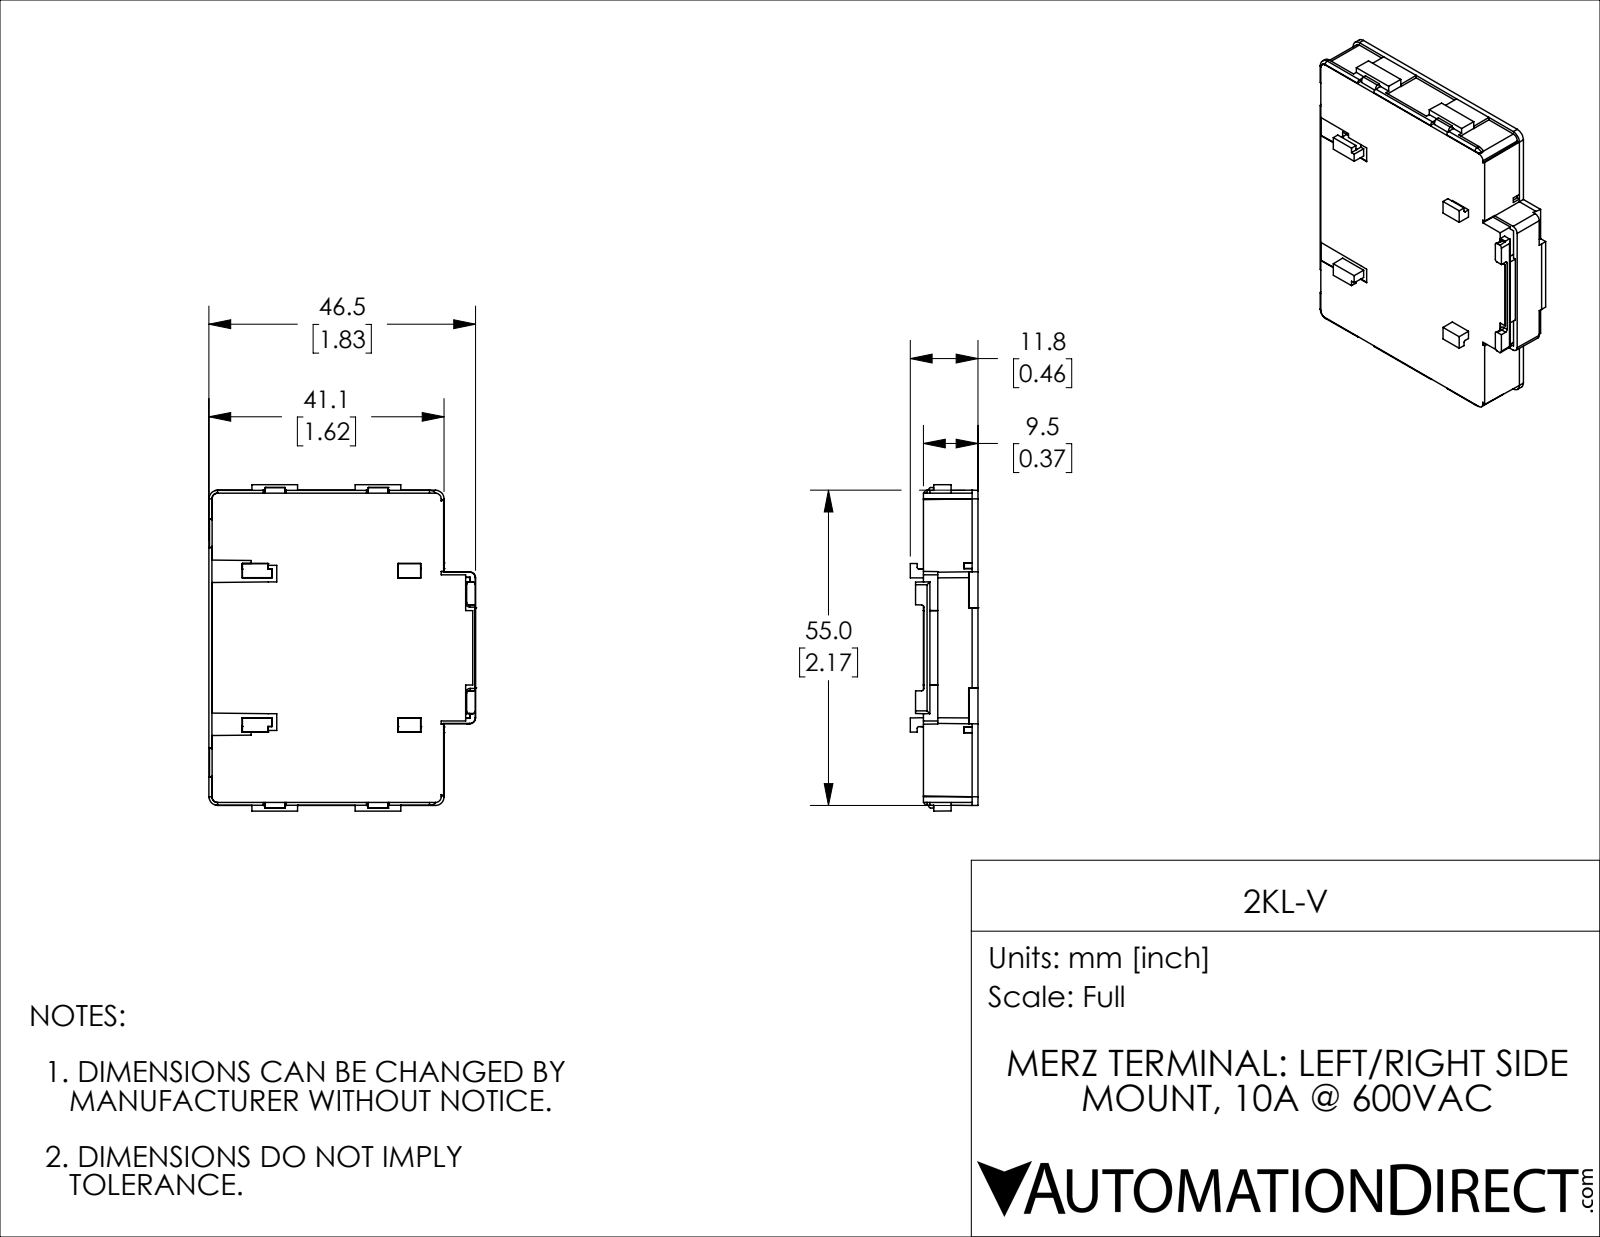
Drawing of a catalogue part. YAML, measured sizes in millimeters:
part_name: "2KL-V"
step_written_by: "SolidWorks 2019 (AUTOMOTIVE_DESIGN)"
units: millimeters
bodies: {solids: 1, faces: 375, planar: 313, cylindrical: 40, other: 22}
overall_size: [57, 46.6, 11.8]
volume: 22450
surface_area: 7587
partial_cylinders:
  - {radius: 0.4, count: 7}
  - {radius: 0.5, count: 6}
  - {radius: 1, count: 6}
  - {radius: 0.3, count: 4}
  - {radius: 0.8, count: 2}
face_to_face_distances: [9.5, 1, 5.5, 54, 8.5, 8.4, 1.1, 55.9, 4.7, 14.2]
